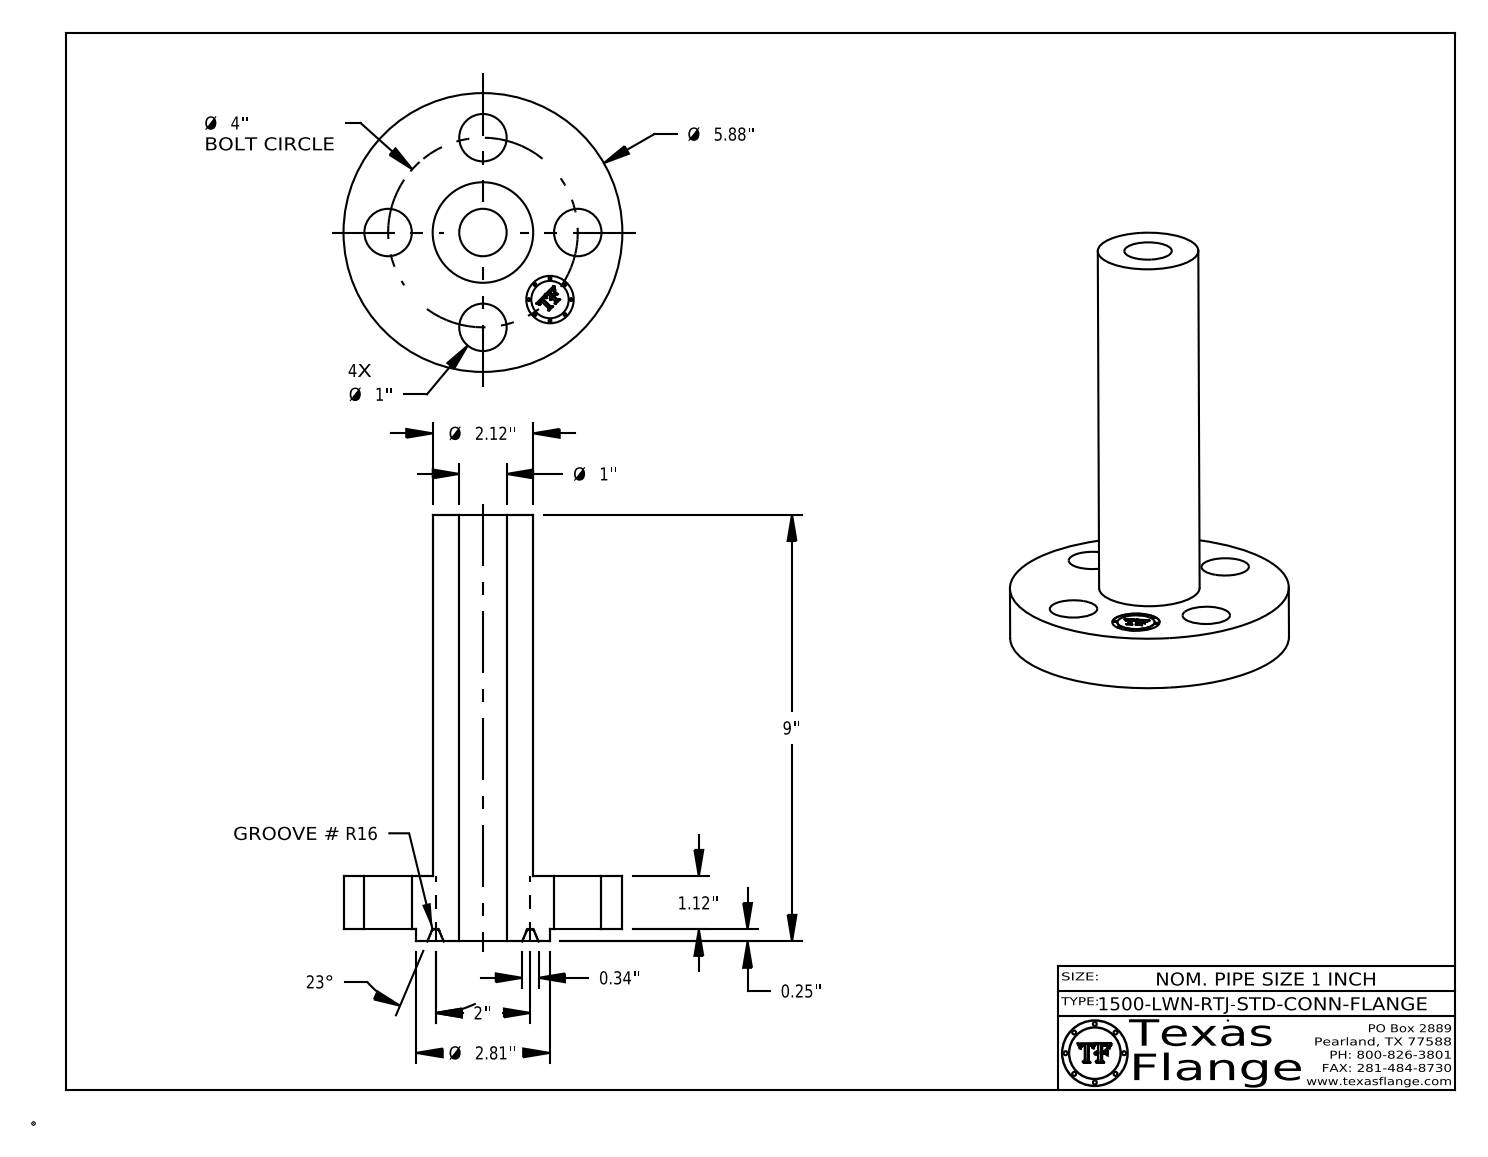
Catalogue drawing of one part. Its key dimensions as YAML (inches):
part_name: "1-1500-LWN-RTJ-STD-CONN-FLANGE"
step_written_by: "CATIA V5 STEP AP214 (AUTOMOTIVE_DESIGN)"
units: inches
bodies: {solids: 1, faces: 415, planar: 371, cylindrical: 36, other: 8}
overall_size: [9, 5.88, 5.88]
volume: 47.94
surface_area: 164.6
round_holes:
  - {diameter: 1, count: 6}
round_bosses_or_shafts:
  - {diameter: 0.061, count: 8}
  - {diameter: 5.88, count: 1}
  - {diameter: 2.813, count: 1}
  - {diameter: 2.12, count: 1}
  - {diameter: 0.788, count: 1}
face_to_face_distances: [1.12, 0.25, 1.37, 9, 8.75, 7.63, 1.365, 1.115, 7.635, 0.298]
hole_center_spacings: [2, 2.828, 1.531, 3.695, 4]
